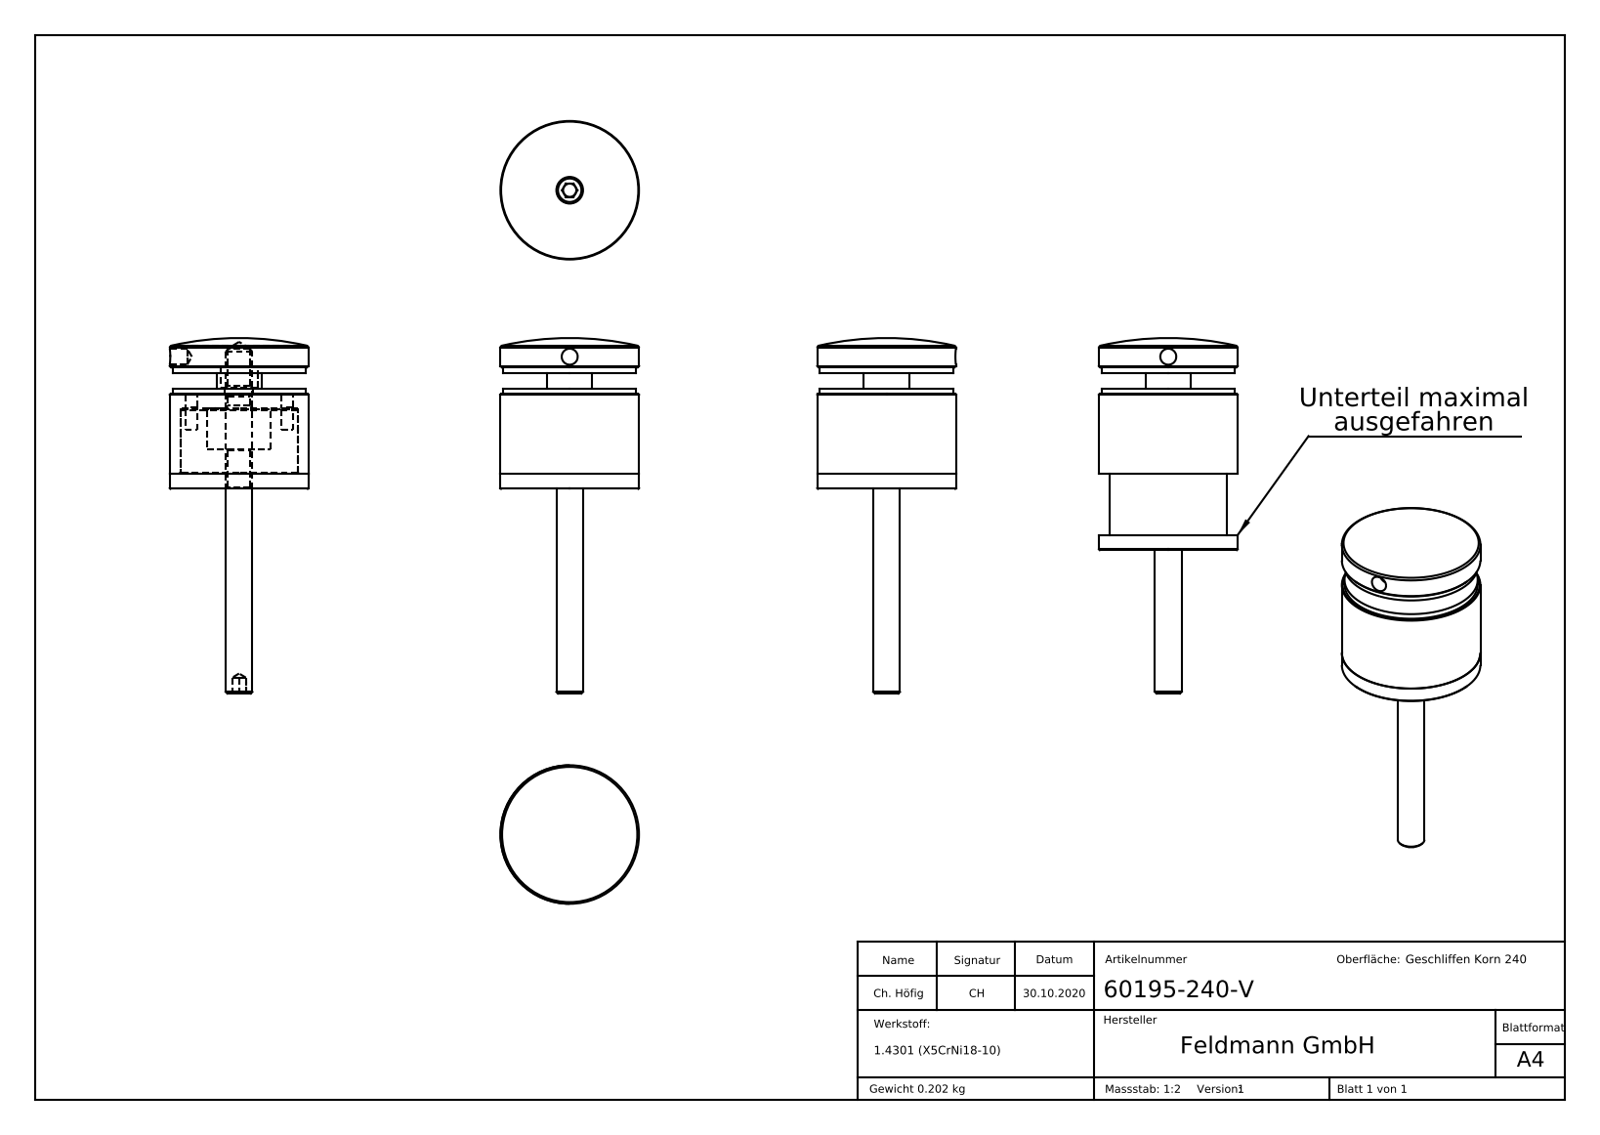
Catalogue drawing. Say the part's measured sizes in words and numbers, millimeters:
The part is named "60195-240-V Teil4; 60195-240-V Teil2_60195-240-V Teil2; 60195-240-V Teil5; 60195-240-V (+8 more)". Its 3-D file was written by "SolidWorks 2018 (CONFIG_CONTROL_DESIGN)". It is 6 solids with 632 faces: 312 planar, 42 cylindrical and 278 other. Overall it measures 135.44 by 52 by 52 millimeters. Its volume is 104 781 cubic millimeters and its surface area 42 068 square millimeters. Round holes: 2 of diameter 4.4, 2 of diameter 4.5, 1 of diameter 6, 1 of diameter 8.5, 1 of diameter 10.5, 1 of diameter 14, 1 of diameter 24, 1 of diameter 44.1. Round bosses or shafts: 1 of diameter 52, 1 of diameter 50, 1 of diameter 44, 1 of diameter 17, 1 of diameter 10. The main face-to-face distances are 8, 2, 10, 58.6, 68.6, 60.6, 6, 66.6, 28.6, 30. The hole center spacings are 18, 36.
